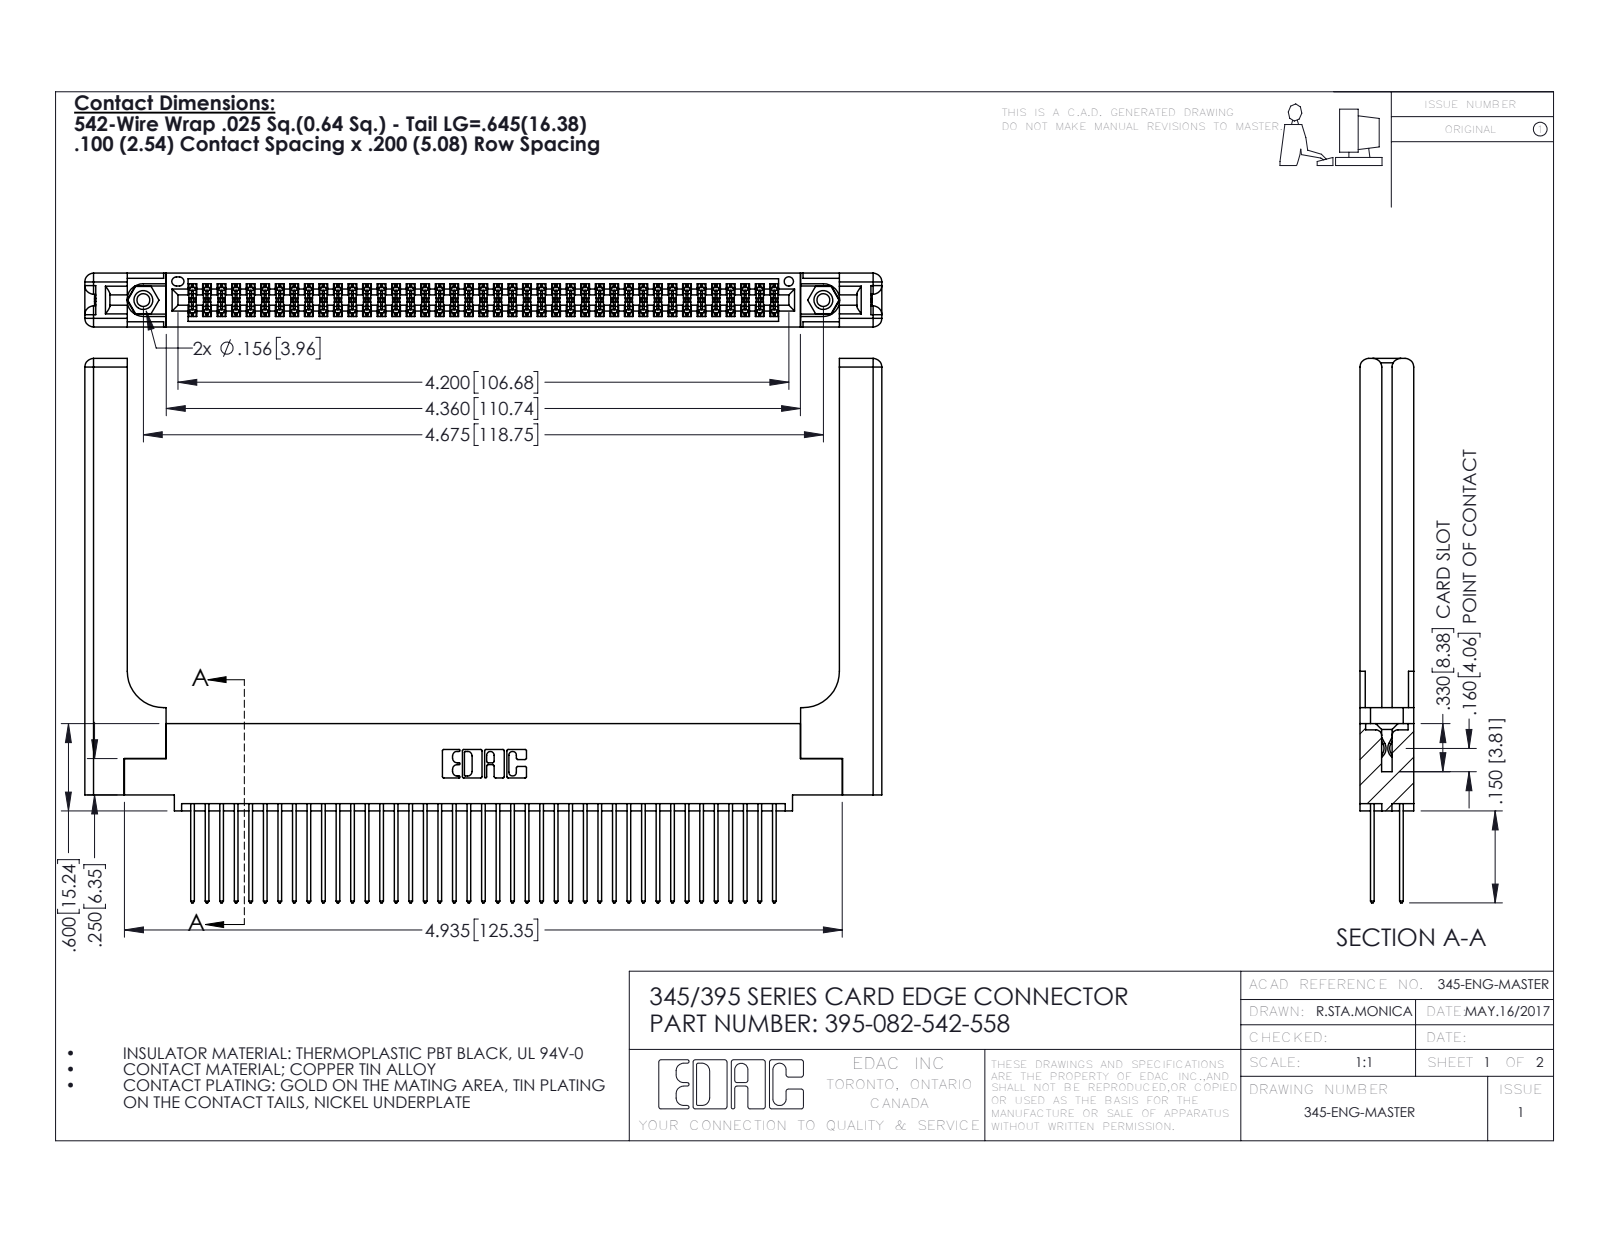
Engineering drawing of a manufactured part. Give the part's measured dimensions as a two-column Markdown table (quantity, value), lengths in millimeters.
| quantity | value |
| --- | --- |
| part name | 345-250-001_345-250-001-102; 395-082-542-558; 345 Part_0.110 Offset - 0.156 Dia-TH; 345-220-058_345-220-058 (+1 more) |
| STEP written by | SolidWorks 2016 (CONFIG_CONTROL_DESIGN) |
| units | millimeters |
| bodies | 87 solids, 4486 faces (2938 planar, 1488 cylindrical, 60 other) |
| overall size | 139.2 × 95 × 9.4 |
| volume | 22 290 mm³ |
| surface area | 27 340 mm² |
| round holes (diameter × count) | 2.3 × 2, 3.2 × 2, 4 × 2, 1.6 × 1 |
| round bosses / shafts (diameter × count) | 3.9 × 2 |
| partial cylindrical surfaces (radius × count) | 0.2 × 123, 0.3 × 82, 0.3 × 22, 1.5 × 16, 0.2 × 6, 0.8 × 6, 0.7 × 3, 0.4 × 2 |
| main face-to-face distances | 1.8, 7.6, 9.4, 5.1, 2.5, 6.9, 0.6, 5.7, 4.4, 3.8 |
| hole center spacings | 6.9, 112.8, 118.7 |
